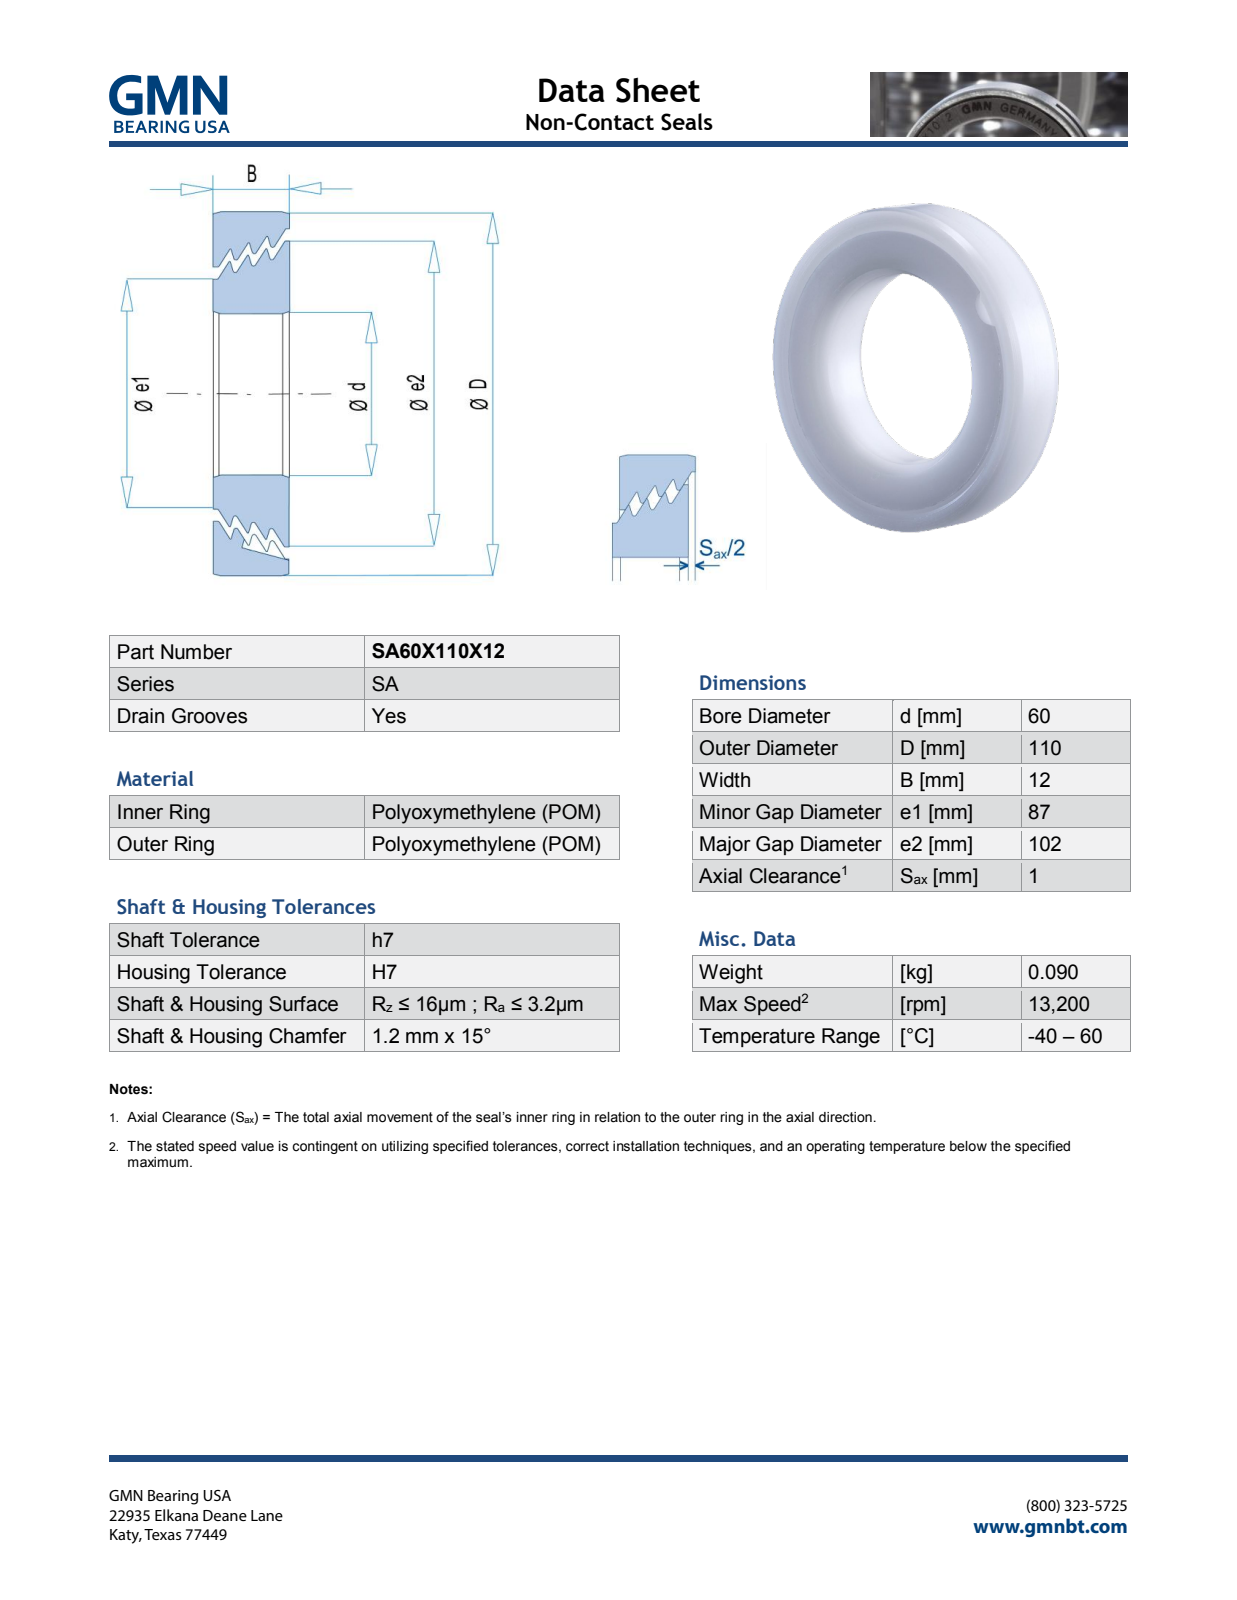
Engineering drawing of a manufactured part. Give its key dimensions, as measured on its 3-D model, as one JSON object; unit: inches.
{"part_name": "SA60X110X12_PRT", "step_written_by": "PRO/ENGINEER BY PARAMETRIC TECHNOLOGY CORPORATION, 2013150 (AUTOMOTIVE_DESIGN)", "units": "inches", "bodies": {"solids": 2, "faces": 653, "planar": 580, "cylindrical": 13, "other": 60}, "overall_size": [4.331, 4.331, 0.475], "volume_in3": 4.697, "surface_area_in2": 52.41, "round_holes": [[2.362, 1], [3.489, 1], [4.08, 1]], "round_bosses_or_shafts": [[4.331, 1], [4.016, 1], [3.425, 1]], "partial_cylinders_radius": [[0.236, 1]], "face_to_face_distances": [0.472, 0.475, 0.258, 0.255, 0.217, 0.03, 0.03, 0.237, 0.03, 0.208]}
